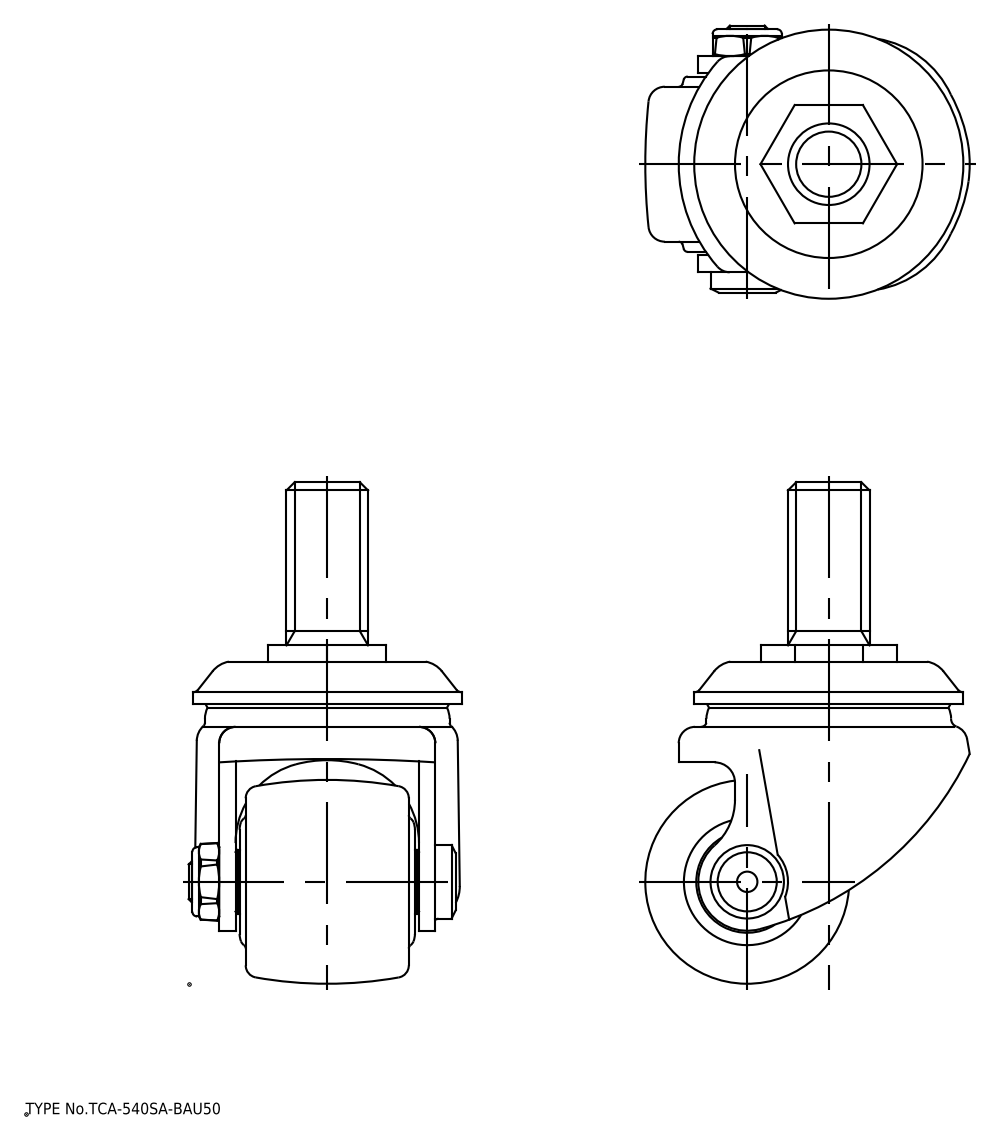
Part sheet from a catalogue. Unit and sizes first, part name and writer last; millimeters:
Units: millimetres
Overall size (bounding box): 123 × 78.73 × 69.5
Round holes (diameter × count): ⌀10.2 ×1, ⌀23 ×1, ⌀26.47 ×1, ⌀54.3 ×1
Round bosses / shafts (diameter × count): ⌀66 ×1, ⌀60 ×1, ⌀20 ×1, ⌀18 ×1, ⌀17 ×1, ⌀15.6 ×1, ⌀10 ×1
Partial cylindrical surfaces — rounded edges, fillets, slot ends (radius × count): R5 ×3, R2 ×2, R6 ×1, R9.1 ×1, R12 ×1, R15 ×1, R31.5 ×1, R80 ×1
Main face-to-face distances: 4, 20, 42.5, 2.5, 6.5, 46.5, 49, 4.5, 24.5, 40
Volume: 176 481 mm³ · Surface area: 37 688 mm²
Bodies: 2 solids, 167 faces (40 planar, 45 cylindrical, 82 other)
Part name (STEP PRODUCT): wheel
STEP written by: spGate 19.8.4 (****-****-****-****) (AUTOMOTIVE_DESIGN)
